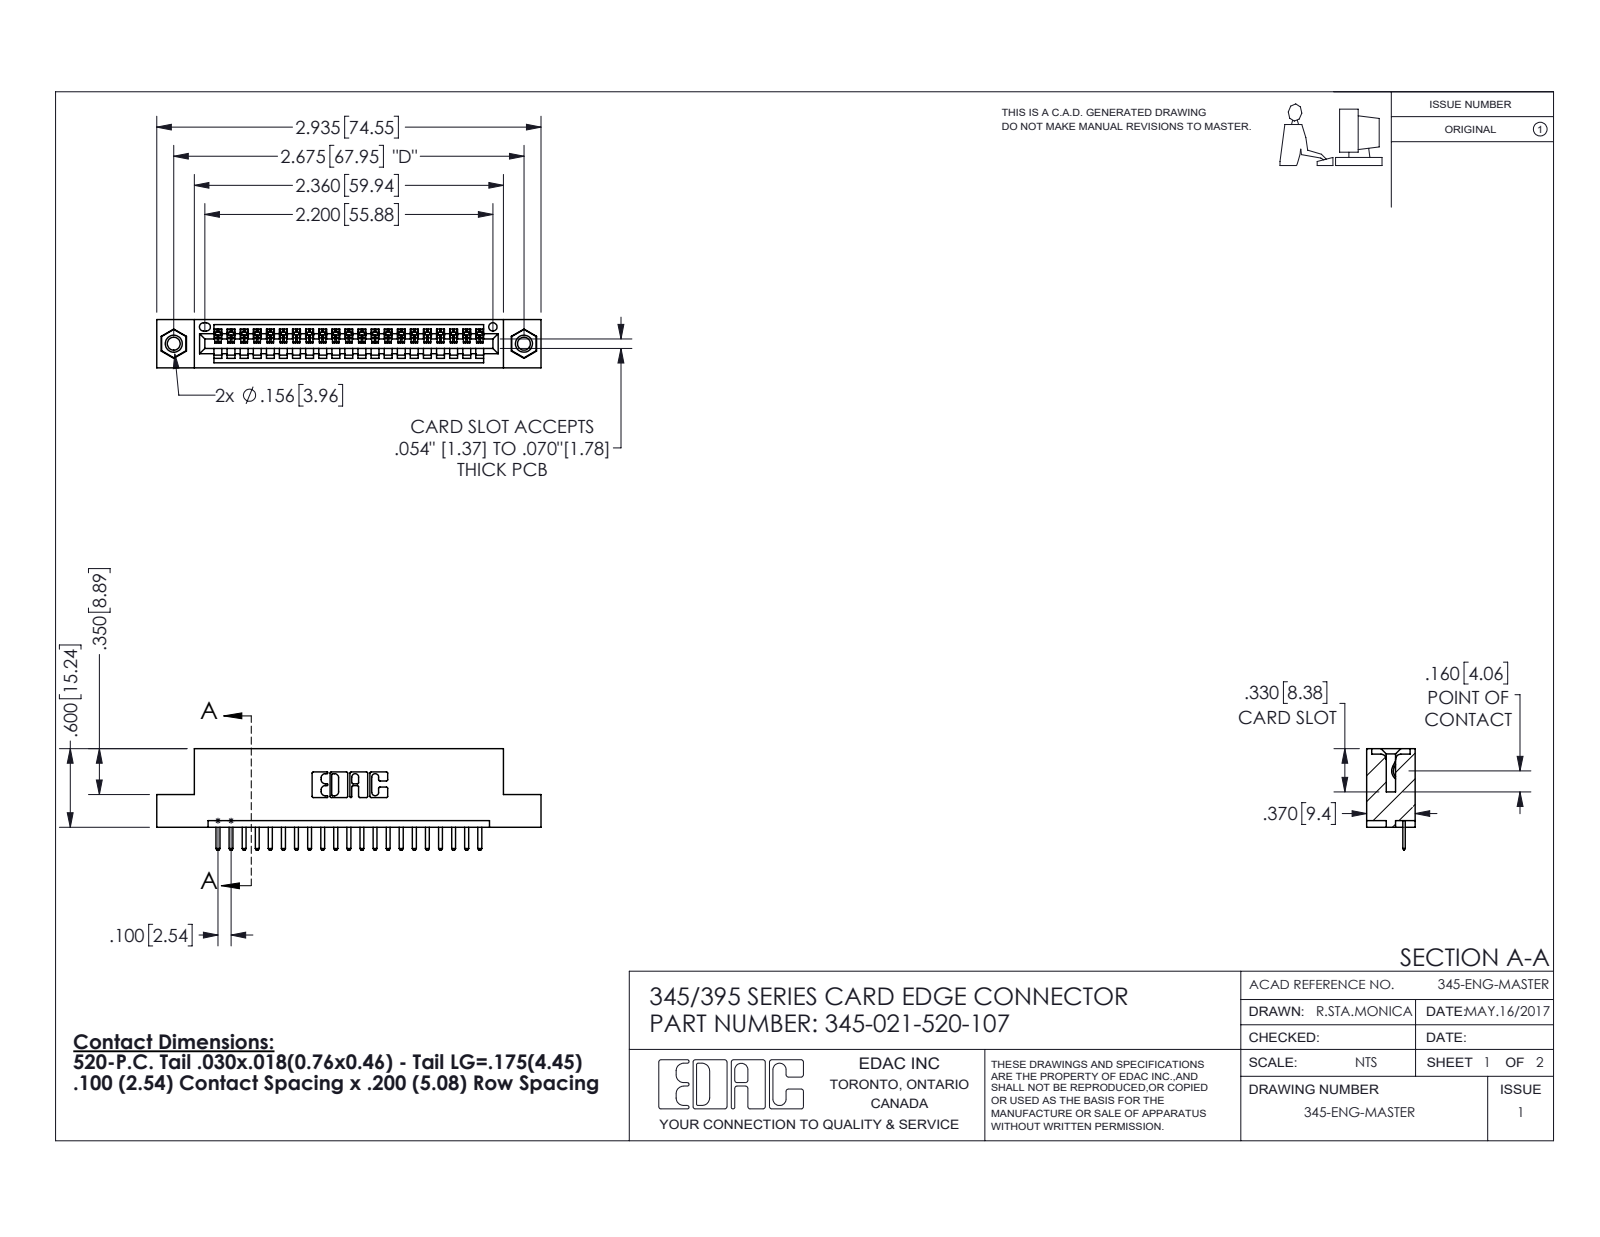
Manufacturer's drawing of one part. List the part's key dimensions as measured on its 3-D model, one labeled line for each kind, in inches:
Part name (STEP PRODUCT): 345-292-001_345-293-120; 345 Part_Flush Mounting Lugs - 0.156 Dia-TI; 345-250-001_345-250-005-103; 345-021-520-107
STEP written by: SolidWorks 2016 (CONFIG_CONTROL_DESIGN)
Units: inches
Bodies: 24 solids, 1488 faces (994 planar, 478 cylindrical, 16 other)
Overall size (bounding box): 2.935 × 0.775 × 0.37
Volume: 0.417 in³ · Surface area: 13.38 in²
Round holes (diameter × count): ⌀0.098 ×2, ⌀0.125 ×2, ⌀0.156 ×2, ⌀0.064 ×1
Round bosses / shafts (diameter × count): ⌀0.155 ×2
Partial cylindrical surfaces — rounded edges, fillets, slot ends (radius × count): R0.01 ×44, R0.006 ×42, R0.01 ×22, R0.007 ×6, R0.031 ×6, R0.026 ×3, R0.031 ×2, R0.04 ×2
Main face-to-face distances: 0.072, 0.298, 0.2, 0.37, 0.098, 0.272, 0.025, 0.225, 0.072, 0.149
Hole centre spacings: 0.27, 2.441, 2.675
